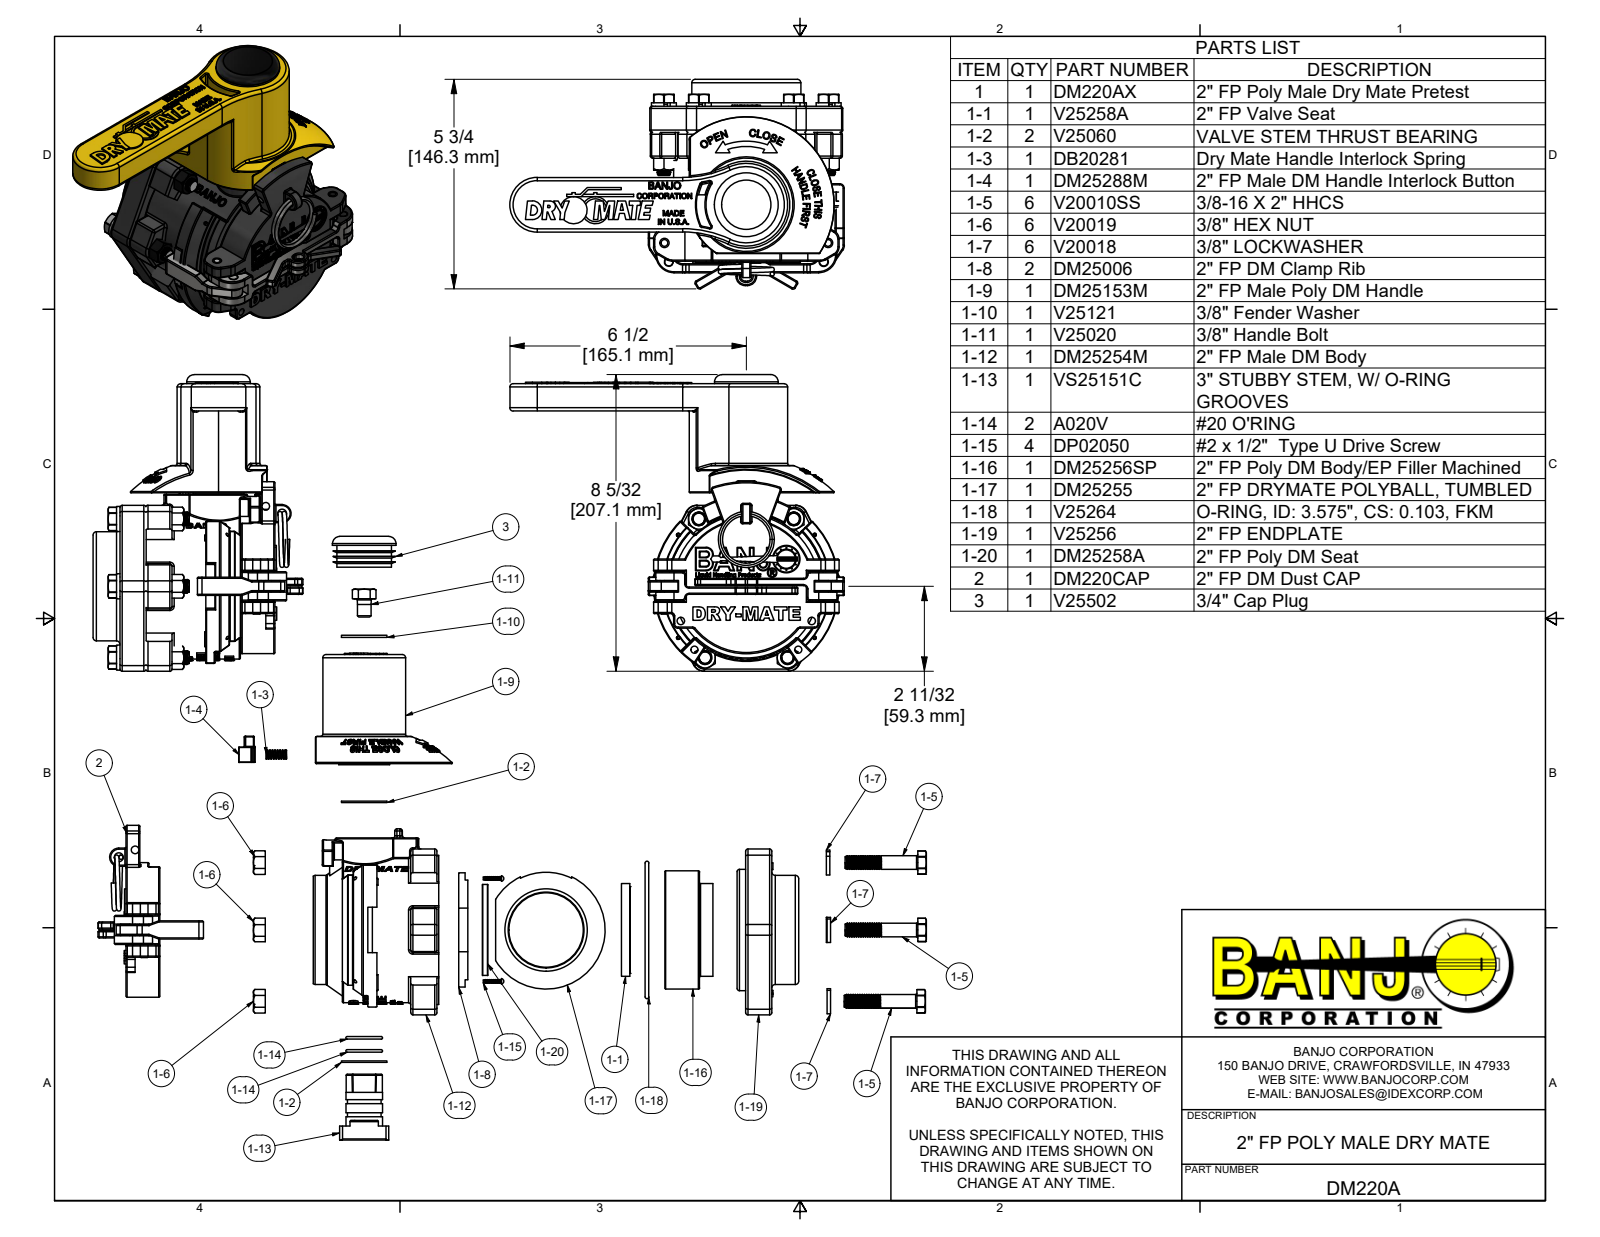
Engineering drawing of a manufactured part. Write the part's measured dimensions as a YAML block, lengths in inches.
part_name: "DM25254MX; DM25254MY; DM25254M; DM25153M (+8 more)"
step_written_by: "Autodesk Inventor 2014 (AUTOMOTIVE_DESIGN)"
units: inches
bodies: {solids: 53, faces: 5814, planar: 2077, cylindrical: 1425, other: 2312}
overall_size: [9.193, 8.155, 5.778]
volume: 65.91
surface_area: 585
round_holes:
  - {diameter: 0.406, count: 7}
  - {diameter: 0.307, count: 6}
  - {diameter: 0.385, count: 6}
  - {diameter: 0.25, count: 5}
  - {diameter: 0.086, count: 4}
  - {diameter: 0.13, count: 4}
  - {diameter: 0.2, count: 4}
  - {diameter: 0.26, count: 3}
  - {diameter: 2.05, count: 2}
  - {diameter: 0.21, count: 1}
  - {diameter: 0.307, count: 1}
  - {diameter: 0.508, count: 1}
round_bosses_or_shafts:
  - {diameter: 0.324, count: 90}
  - {diameter: 0.375, count: 7}
  - {diameter: 0.687, count: 6}
  - {diameter: 0.082, count: 4}
  - {diameter: 0.26, count: 2}
  - {diameter: 0.257, count: 2}
  - {diameter: 0.249, count: 2}
  - {diameter: 4, count: 1}
partial_cylinders:
  - {radius: 0.03, count: 255}
  - {radius: 0.06, count: 66}
  - {radius: 0.02, count: 30}
  - {radius: 0.01, count: 24}
  - {radius: 0.25, count: 22}
  - {radius: 0.313, count: 13}
  - {radius: 0.063, count: 12}
  - {radius: 0.162, count: 12}
face_to_face_distances: [0.15, 4.11, 4.26, 0.85, 0.66, 3.45, 3.6, 1.5, 0.05, 0.2]
hole_center_spacings: [1.467, 2.35, 4.376, 0.367, 0.47, 0.534, 0.555, 0.719]
